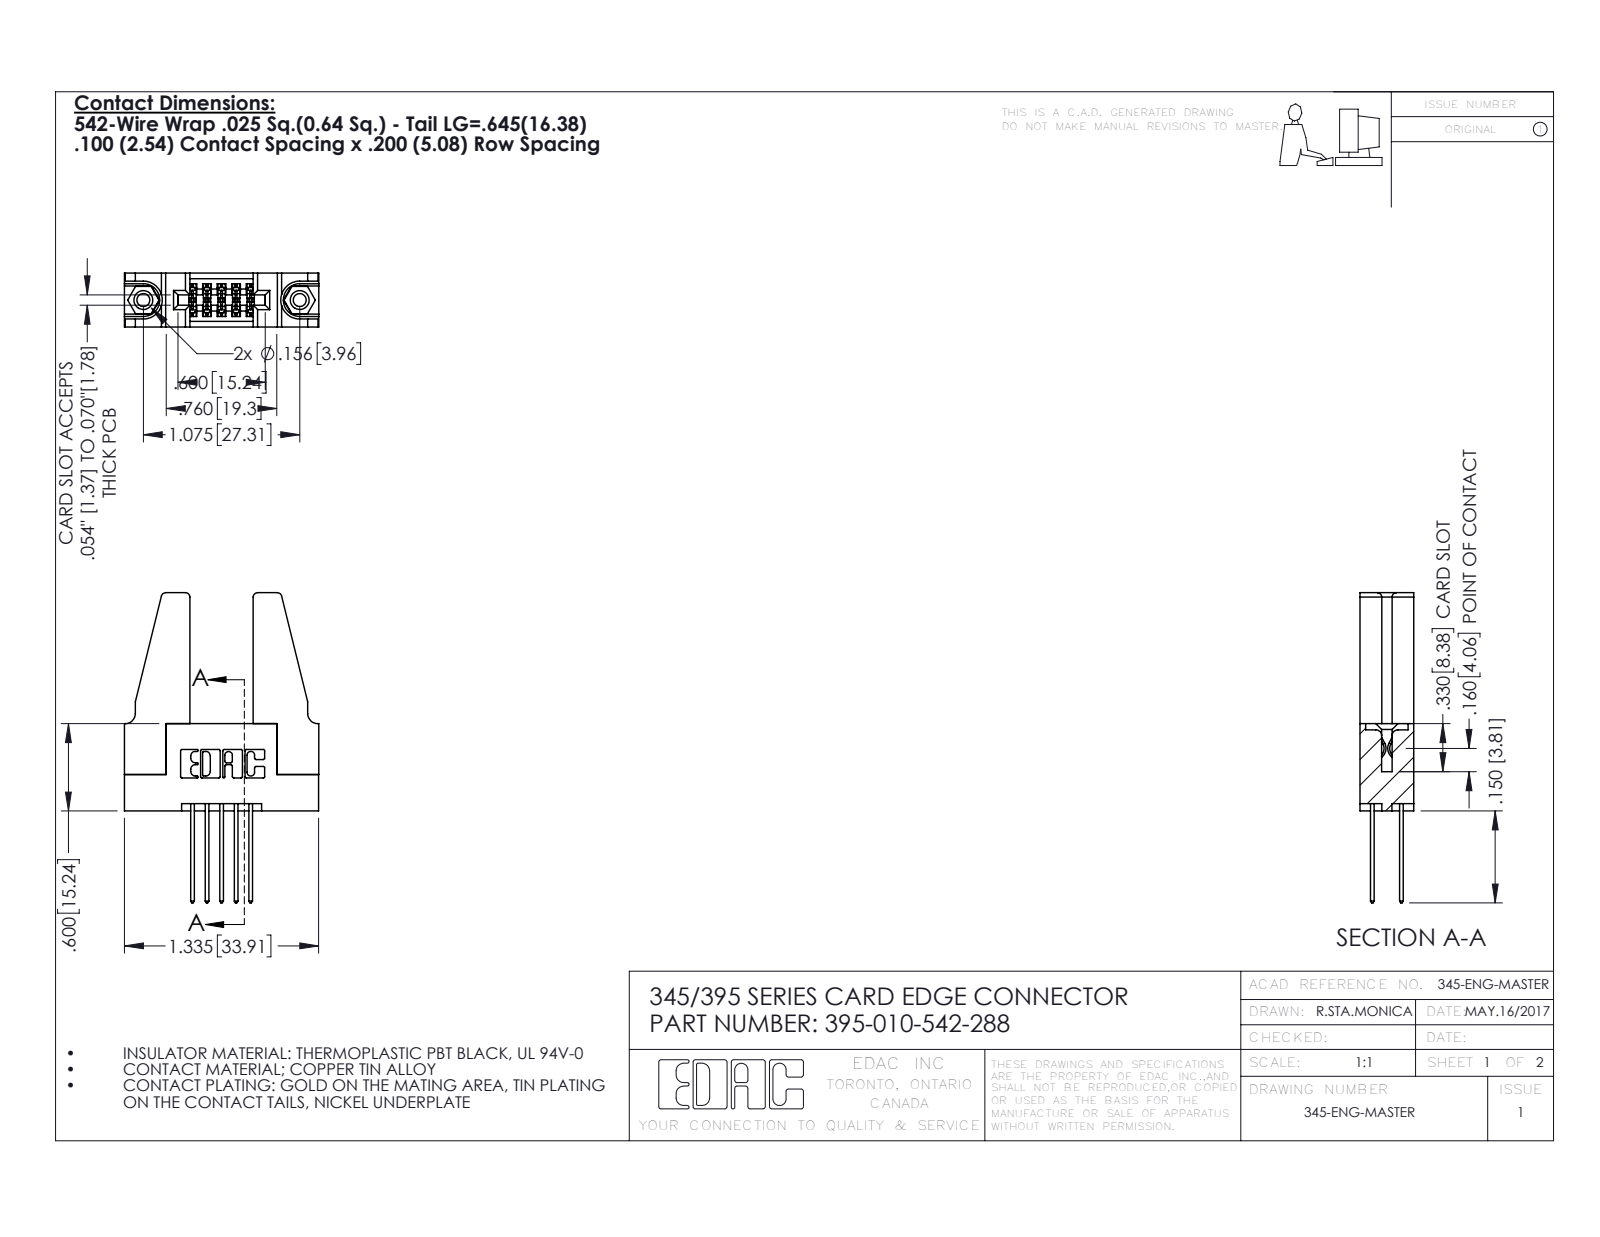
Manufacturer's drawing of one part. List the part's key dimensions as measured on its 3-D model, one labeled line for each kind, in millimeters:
Part name (STEP PRODUCT): 345 Part_Flush Mounting Lugs - 0.156 Dia-TH; 345-250-001_345-250-001-102; 345-292-001_345-293-142; 345-220-078_345-220-088 (+1 more)
STEP written by: SolidWorks 2016 (CONFIG_CONTROL_DESIGN)
Units: millimetres
Bodies: 15 solids, 750 faces (482 planar, 252 cylindrical, 16 other)
Overall size (bounding box): 54.2 × 33.9 × 9.4
Volume: 6 260 mm³ · Surface area: 7 058 mm²
Round holes (diameter × count): ⌀2.3 ×2, ⌀3.2 ×2, ⌀4 ×2, ⌀1.6 ×1
Round bosses / shafts (diameter × count): ⌀3.9 ×2
Partial cylindrical surfaces — rounded edges, fillets, slot ends (radius × count): R0.3 ×22, R0.2 ×15, R0.3 ×10, R0.8 ×8, R0.2 ×6, R0.8 ×6, R0.7 ×3, R0.4 ×2
Main face-to-face distances: 9.4, 1.8, 5.1, 7.6, 2.5, 6.9, 0.6, 5.7, 15.2, 6.4
Hole centre spacings: 6.9, 21.5, 27.3
